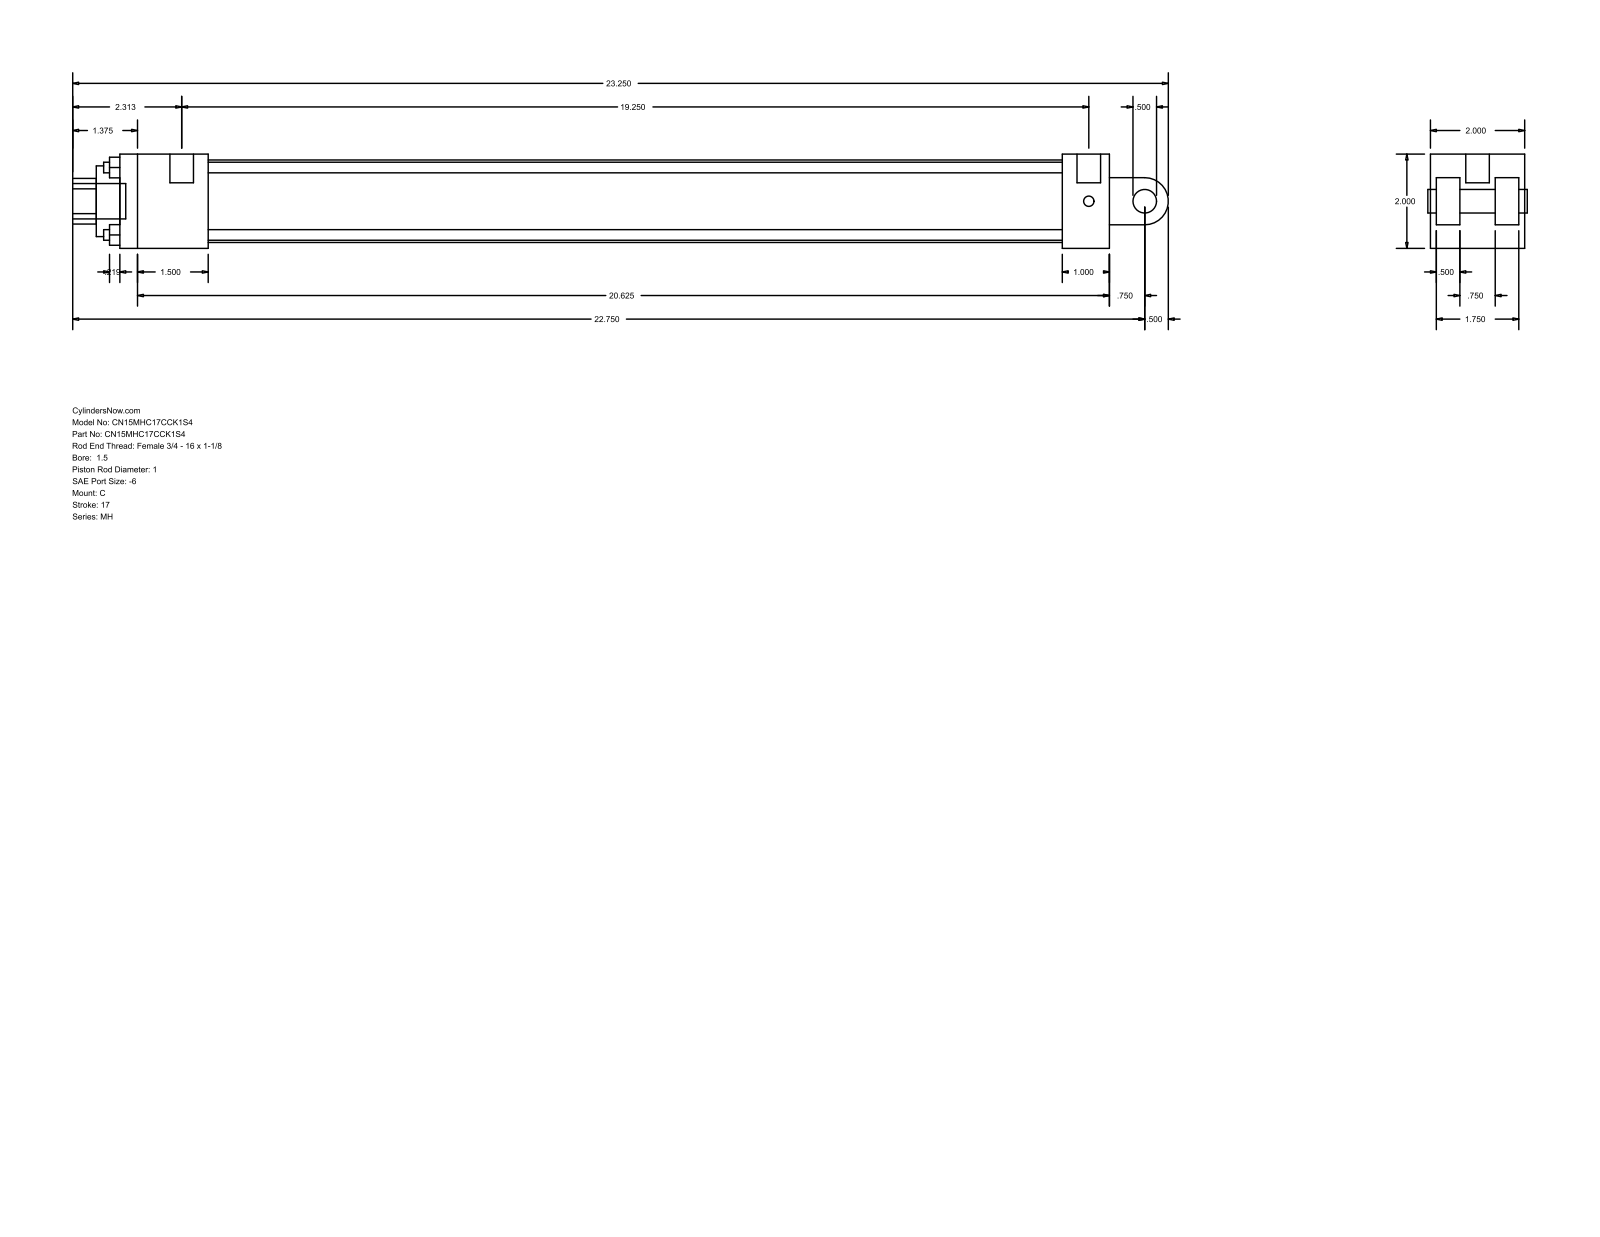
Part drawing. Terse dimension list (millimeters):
name: MH_C__0150_1
written by: GSSL Pune (CONFIG_CONTROL_DESIGN)
unit: mm
bodies: 0 solids, 99 faces (70 planar, 29 cylindrical, 0 other)
size: 590.55 × 50.8 × 50.8
holes: 4× ⌀5.71, 2× ⌀5.56, 1× ⌀12.7, 1× ⌀25.4, 1× ⌀38.1, 1× ⌀44.45
bosses: 2× ⌀12.7, 2× ⌀5.56, 1× ⌀19.05
rounds: 1× R12.29, 1× R12.7
face distances: 50.8, 12.7, 47.63, 3.17, 15.87, 25.4, 34.93, 31.76, 533.4, 38.1
hole spacings: 25.68, 36.32, 51.36
